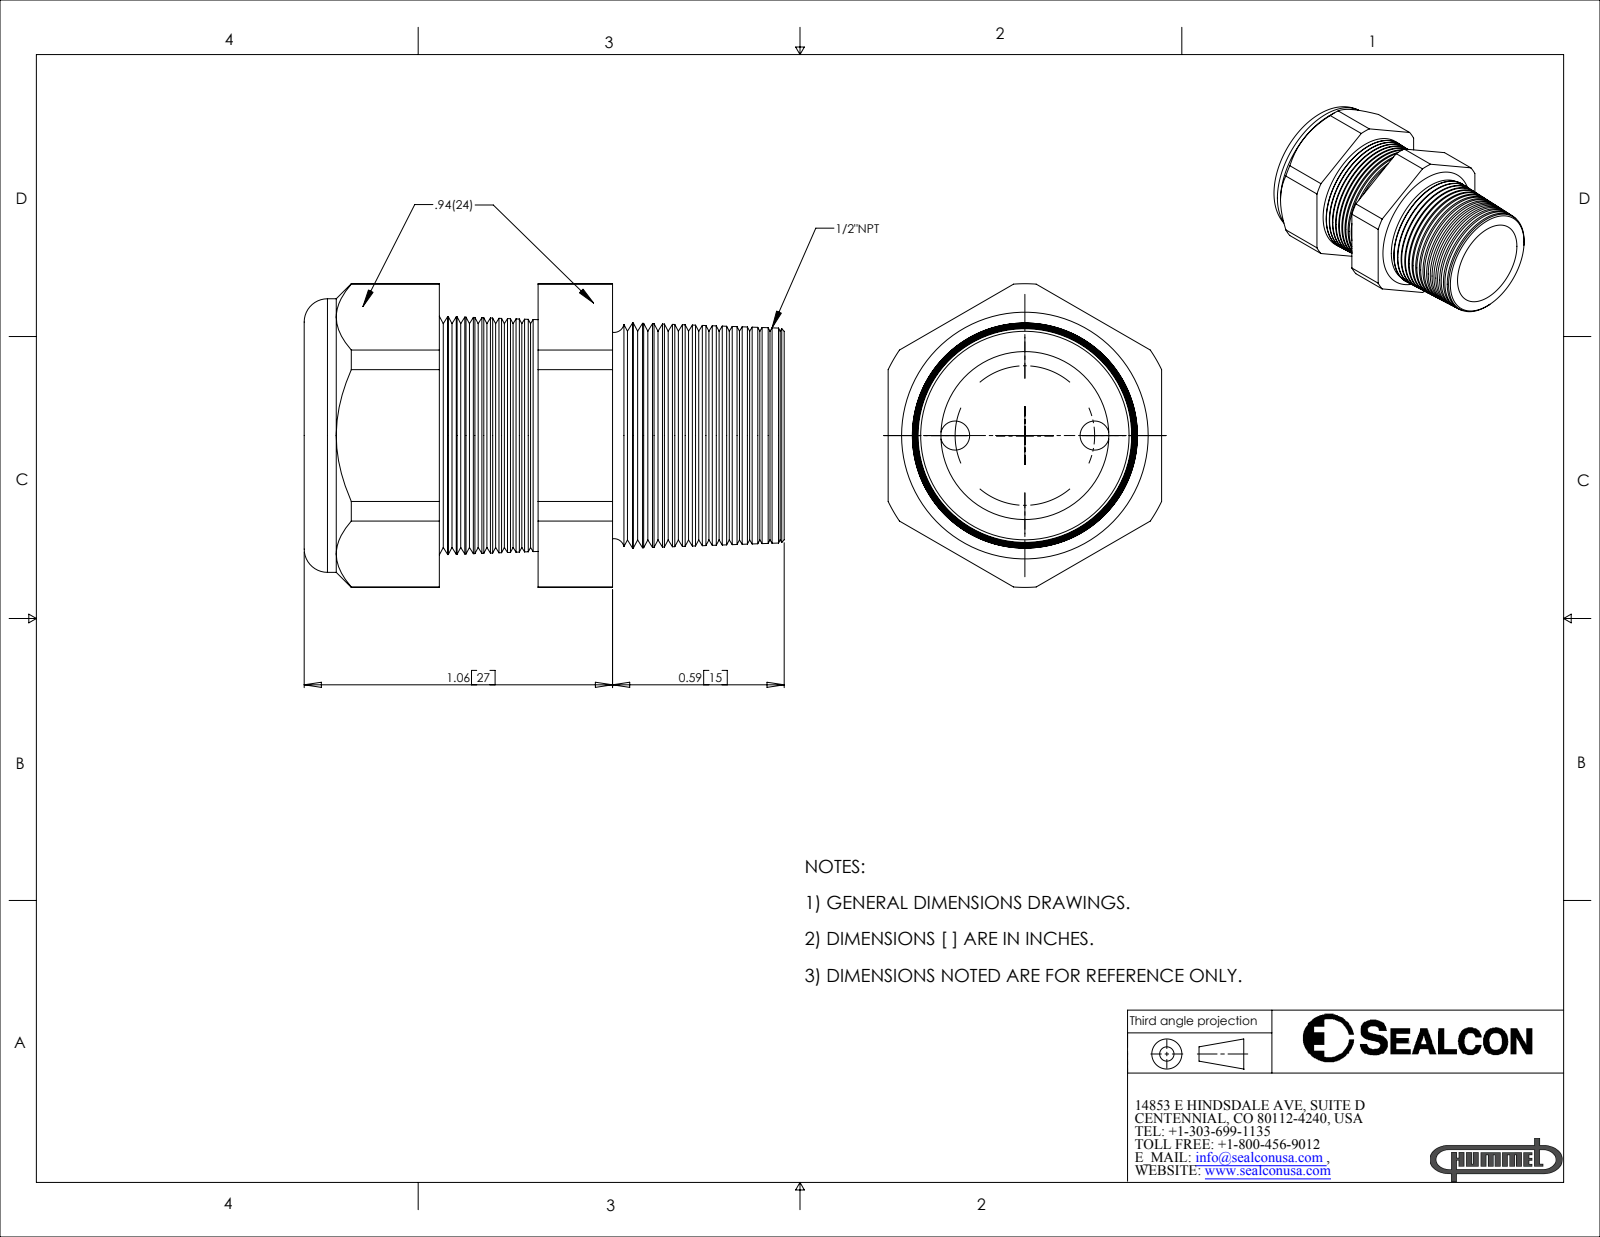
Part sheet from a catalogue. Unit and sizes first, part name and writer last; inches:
Units: inches
Overall size (bounding box): 1.57 × 1.043 × 0.94
Round holes (diameter × count): ⌀0.1 ×2, ⌀0.58 ×1, ⌀0.6 ×1
Round bosses / shafts (diameter × count): ⌀0.94 ×1
Partial cylindrical surfaces — rounded edges, fillets, slot ends (radius × count): R0.522 ×1
Main face-to-face distances: 0.94, 0.454, 0.33, 0.784, 0.444, 0.115, 0.34, 0.02, 0.35, 0.465
Hole centre spacings: 0.24, 0.48
Volume: 0.573 in³ · Surface area: 11.49 in²
Bodies: 2 solids, 208 faces (20 planar, 24 cylindrical, 164 other)
Part name (STEP PRODUCT): CD13N9-GY
STEP written by: SolidWorks 2007 (CONFIG_CONTROL_DESIGN)
